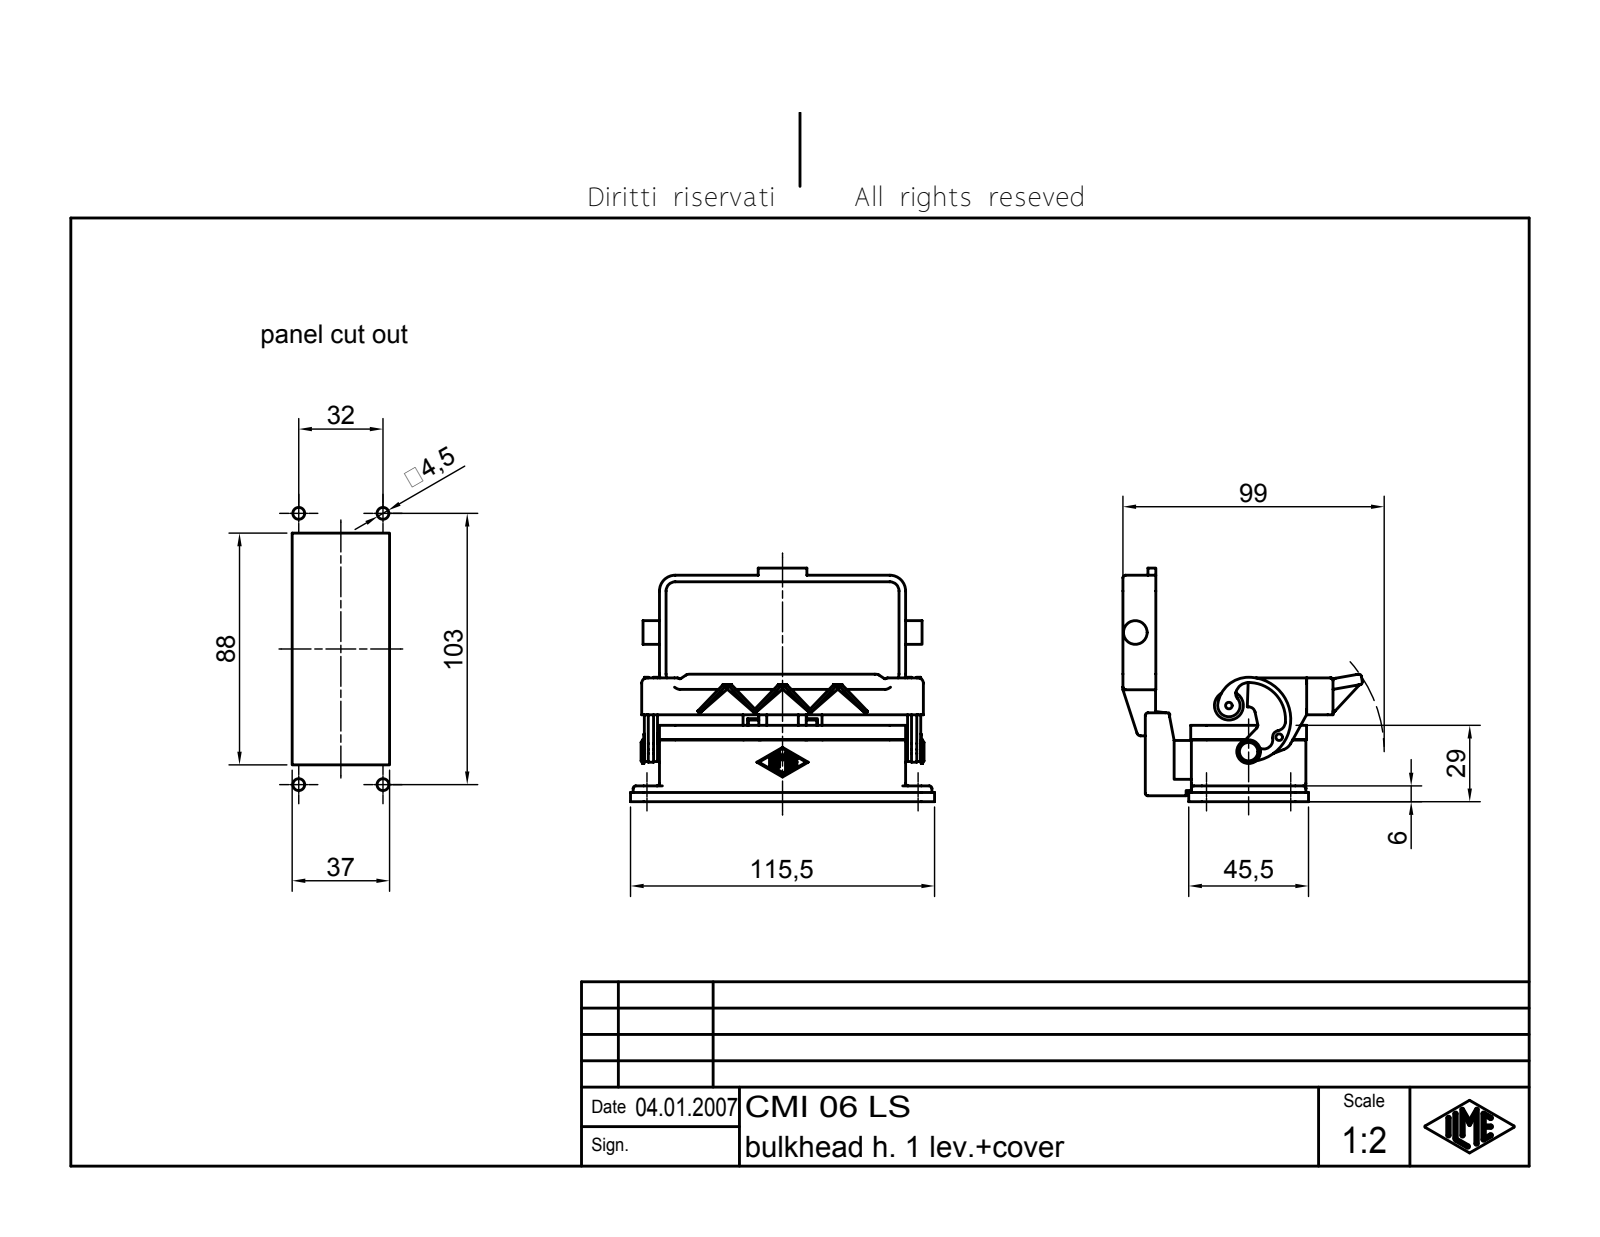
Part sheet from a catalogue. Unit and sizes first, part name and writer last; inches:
Units: inches
Overall size (bounding box): 4.547 × 3.581 × 3.492
Round holes (diameter × count): ⌀0.173 ×4, ⌀0.177 ×4, ⌀0.079 ×1, ⌀0.157 ×1
Round bosses / shafts (diameter × count): ⌀0.354 ×2, ⌀0.197 ×2, ⌀0.433 ×1, ⌀0.276 ×1, ⌀0.157 ×1, ⌀0.118 ×1, ⌀0.098 ×1
Partial cylindrical surfaces — rounded edges, fillets, slot ends (radius × count): R0.039 ×24, R0.015 ×14, R0.079 ×12, R0.236 ×12, R0.098 ×7, R0.138 ×6, R0.197 ×6, R0.157 ×5
Main face-to-face distances: 0.157, 0.118, 0.138, 1.594, 1.142, 1.713, 0.098, 1.004, 0.039, 0.03
Hole centre spacings: 1.26, 4.055, 4.246
Volume: 4.807 in³ · Surface area: 82.32 in²
Bodies: 6 solids, 639 faces (251 planar, 209 cylindrical, 179 other)
Part name (STEP PRODUCT): CMI 06 LS
STEP written by: Autodesk Inventor 7 (AUTOMOTIVE_DESIGN)
